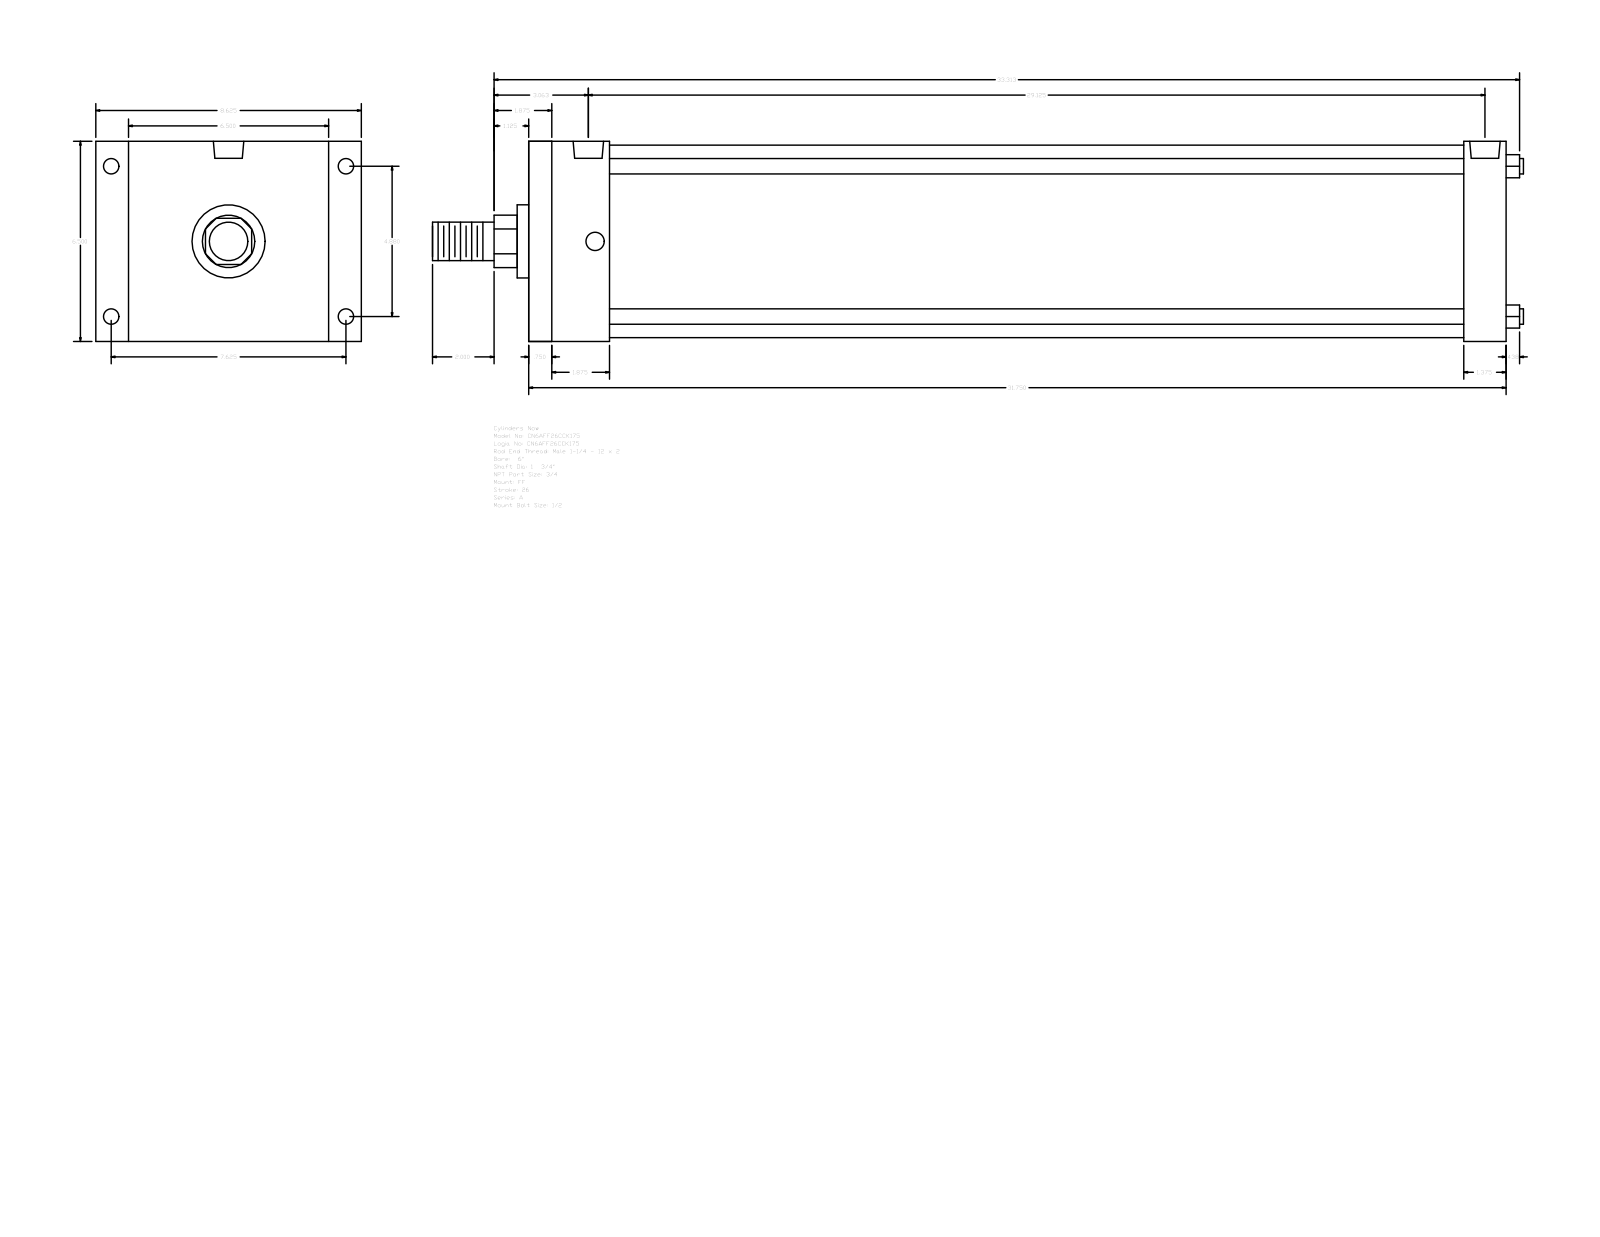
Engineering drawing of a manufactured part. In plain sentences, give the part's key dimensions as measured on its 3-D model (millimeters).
The part is named "A_FF__0600_1.75". Its 3-D file was written by "GSSL Pune (CONFIG_CONTROL_DESIGN)". It is 0 solids with 92 faces: 64 planar, 28 cylindrical and 0 other. Overall it measures 900.11 by 219.07 by 165.1 millimeters. Round holes: 4 of diameter 12.7, 4 of diameter 15.08, 2 of diameter 25.12. Round bosses or shafts: 4 of diameter 12.7, 1 of diameter 158.75, 1 of diameter 60.33, 1 of diameter 44.45, 1 of diameter 31.75. Partial cylindrical surfaces (rounded edges, fillets, slot ends): 1 of radius 21.63. The main face-to-face distances are 165.1, 806.45, 19.05, 787.4, 66.68, 47.63, 739.77, 771.53, 752.48, 704.85. The hole center spacings are 5.56, 123.96, 193.68, 229.95, 728.65, 734.21, 739.77.
